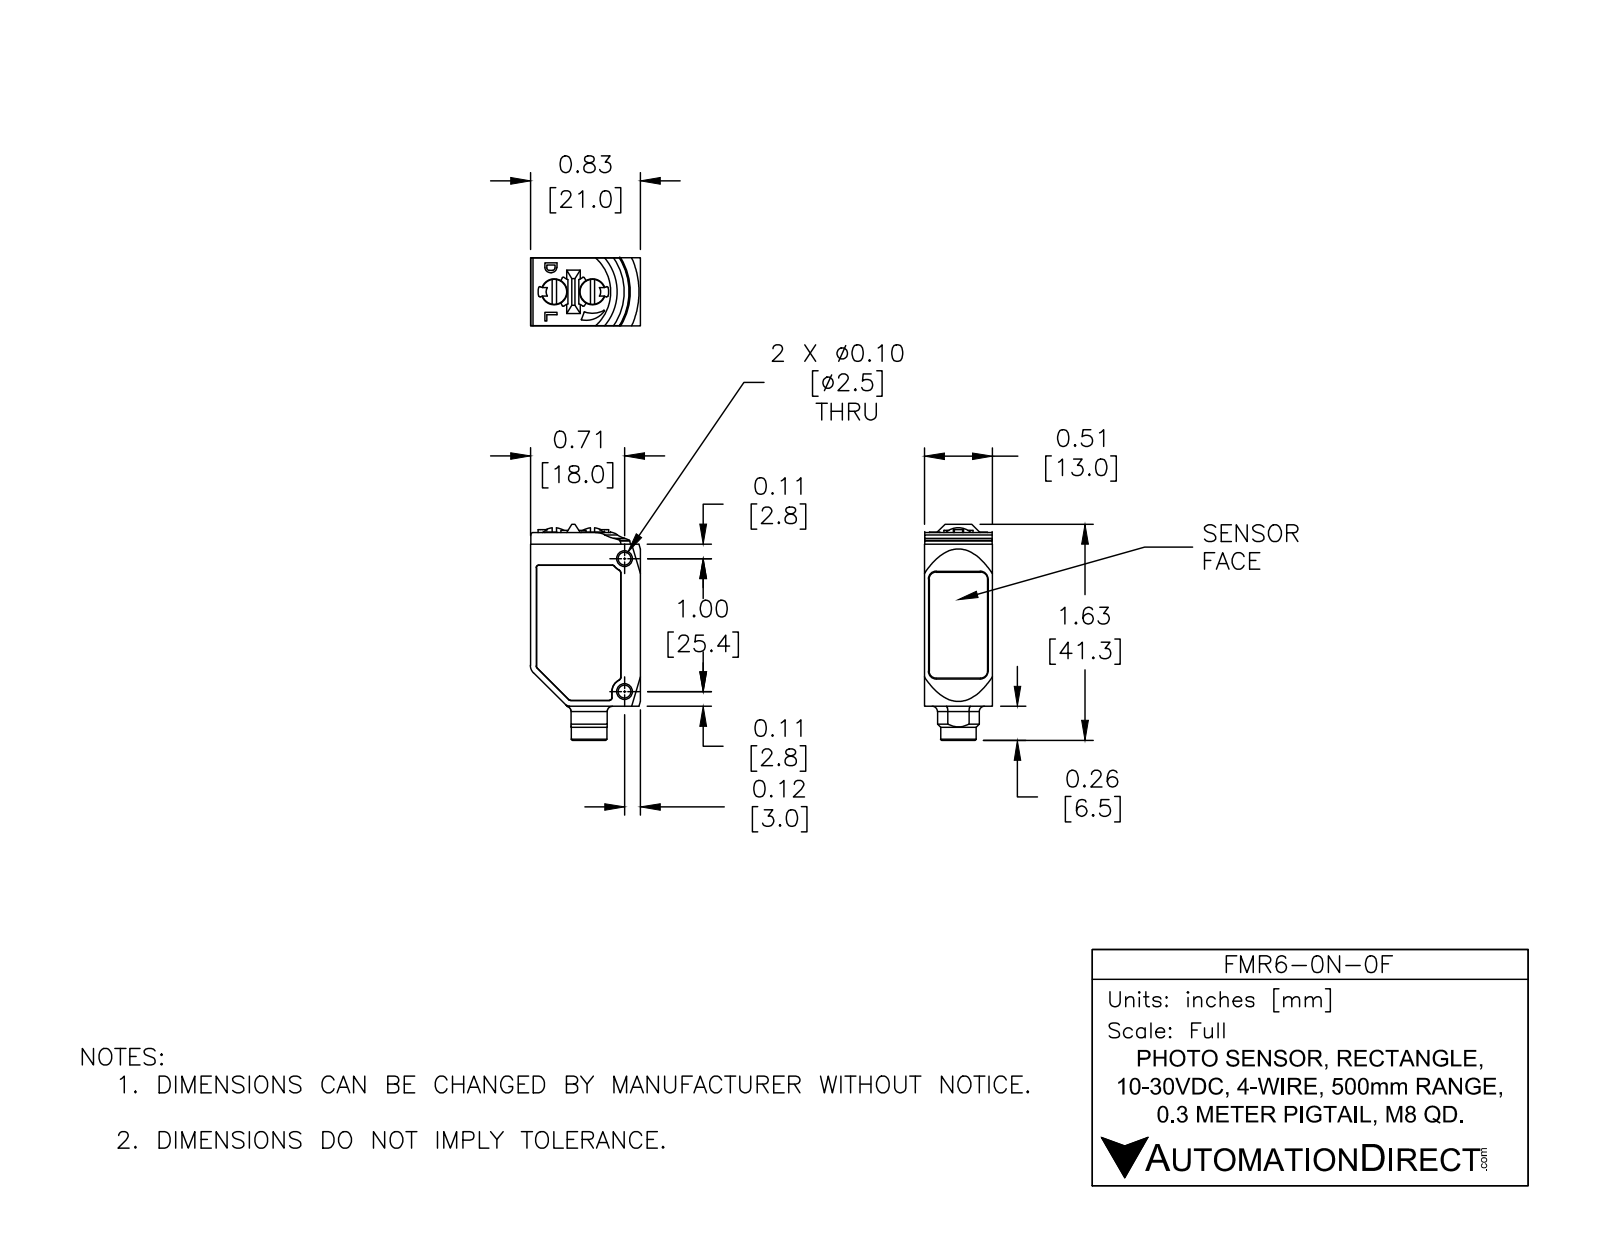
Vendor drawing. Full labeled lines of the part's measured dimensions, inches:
Part name (STEP PRODUCT): FMR6-0N-0F
STEP written by: SolidWorks 2017 (AUTOMOTIVE_DESIGN)
Units: inches
Bodies: 1 solid, 197 faces (89 planar, 79 cylindrical, 29 other)
Overall size (bounding box): 1.626 × 0.827 × 0.512
Volume: 0.527 in³ · Surface area: 5.26 in²
Round holes (diameter × count): ⌀0.097 ×2, ⌀0.197 ×2, ⌀0.228 ×1
Round bosses / shafts (diameter × count): ⌀0.189 ×2, ⌀0.267 ×1
Partial cylindrical surfaces — rounded edges, fillets, slot ends (radius × count): R0.018 ×7, R0.02 ×7, R0.039 ×5, R0.008 ×4, R0.01 ×4, R0.051 ×4, R0.059 ×4, R0.004 ×3
Main face-to-face distances: 0.512, 0.827, 1.307, 0.51, 0.031, 0.48, 0.037, 0.035, 0.474, 0.03
Hole centre spacings: 0.026, 0.262, 0.287, 1
